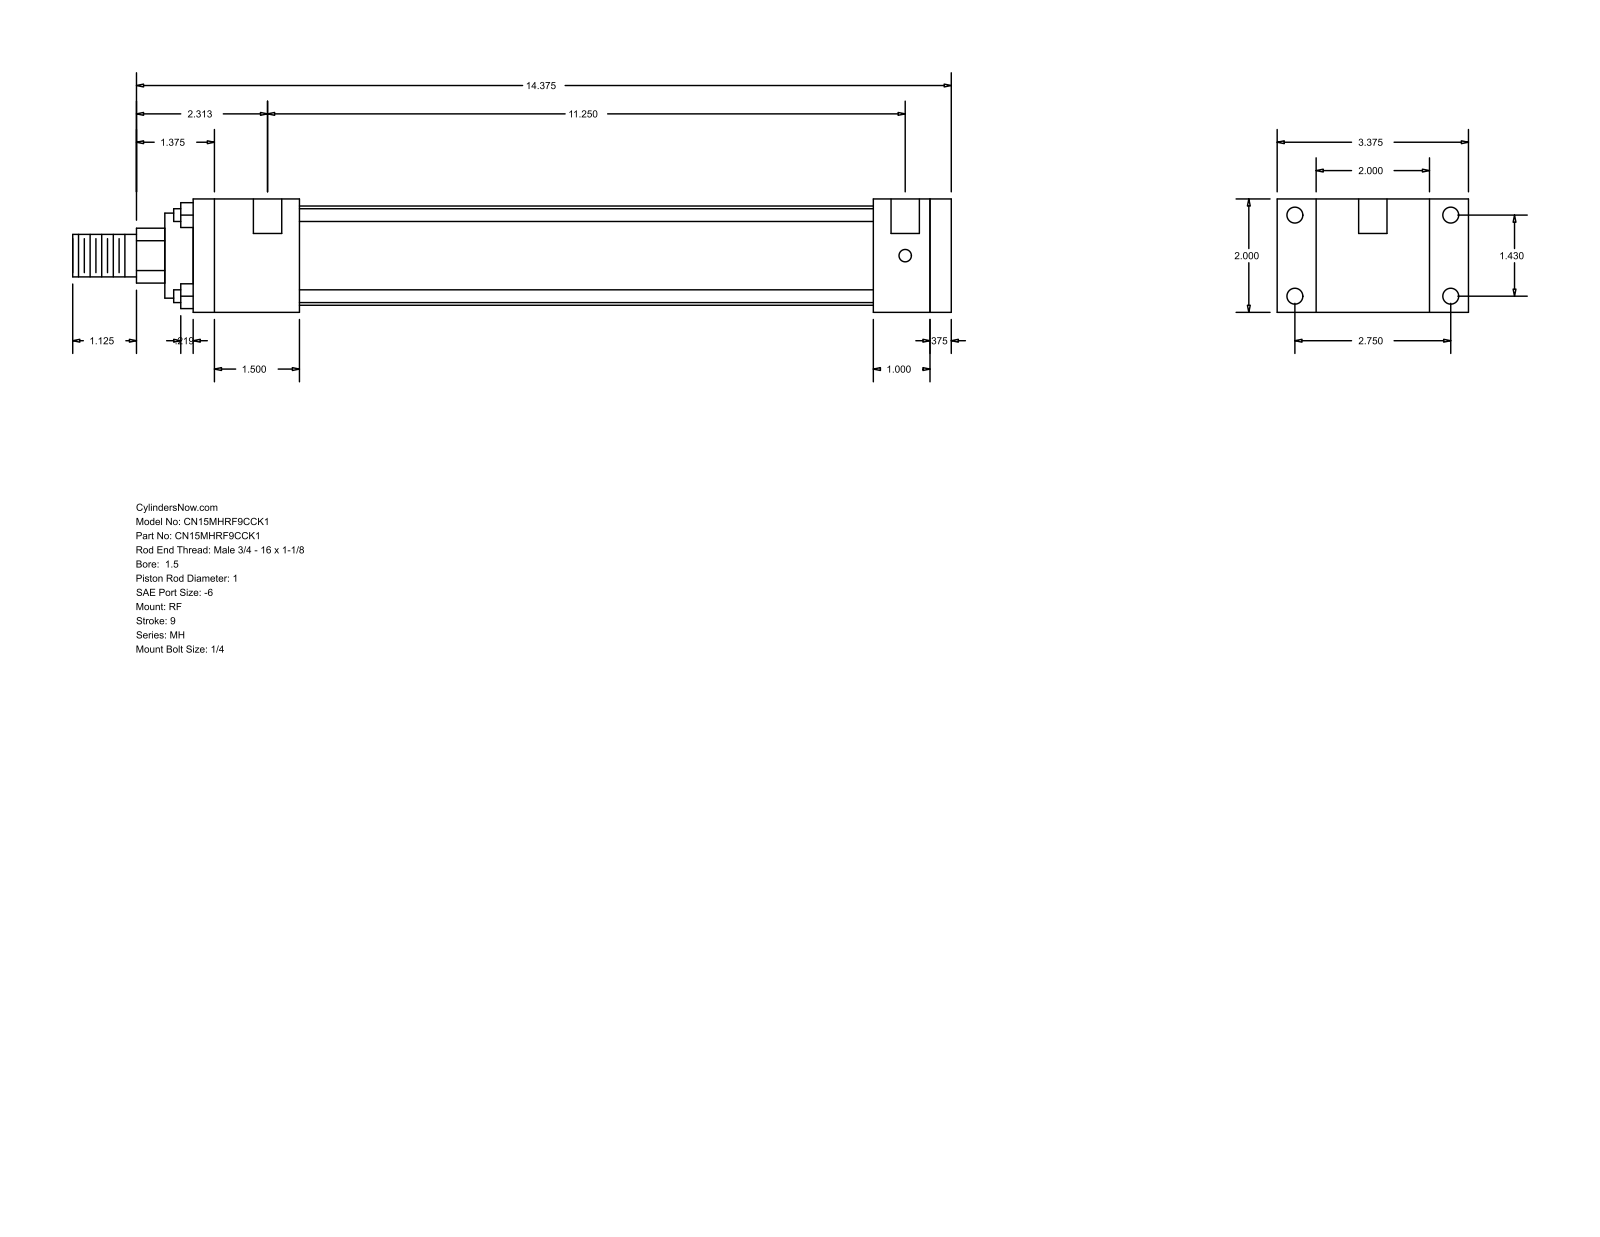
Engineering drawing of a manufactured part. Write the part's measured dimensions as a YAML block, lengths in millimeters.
part_name: "MH_RF__0150_1"
step_written_by: "GSSL Pune (CONFIG_CONTROL_DESIGN)"
units: millimeters
bodies: {solids: 0, faces: 92, planar: 64, cylindrical: 28, other: 0}
overall_size: [393.7, 85.72, 50.8]
round_holes:
  - {diameter: 5.56, count: 4}
  - {diameter: 7.14, count: 4}
  - {diameter: 12.7, count: 2}
round_bosses_or_shafts:
  - {diameter: 5.71, count: 4}
  - {diameter: 44.45, count: 1}
  - {diameter: 38.1, count: 1}
  - {diameter: 25.4, count: 1}
  - {diameter: 19.05, count: 1}
partial_cylinders:
  - {radius: 12.29, count: 1}
face_to_face_distances: [50.8, 9.52, 330.2, 25.4, 339.72, 17.46, 68.26, 304.8, 34.92, 47.63]
hole_center_spacings: [36.32, 69.84, 78.72, 288.93, 3.18, 285.75]
